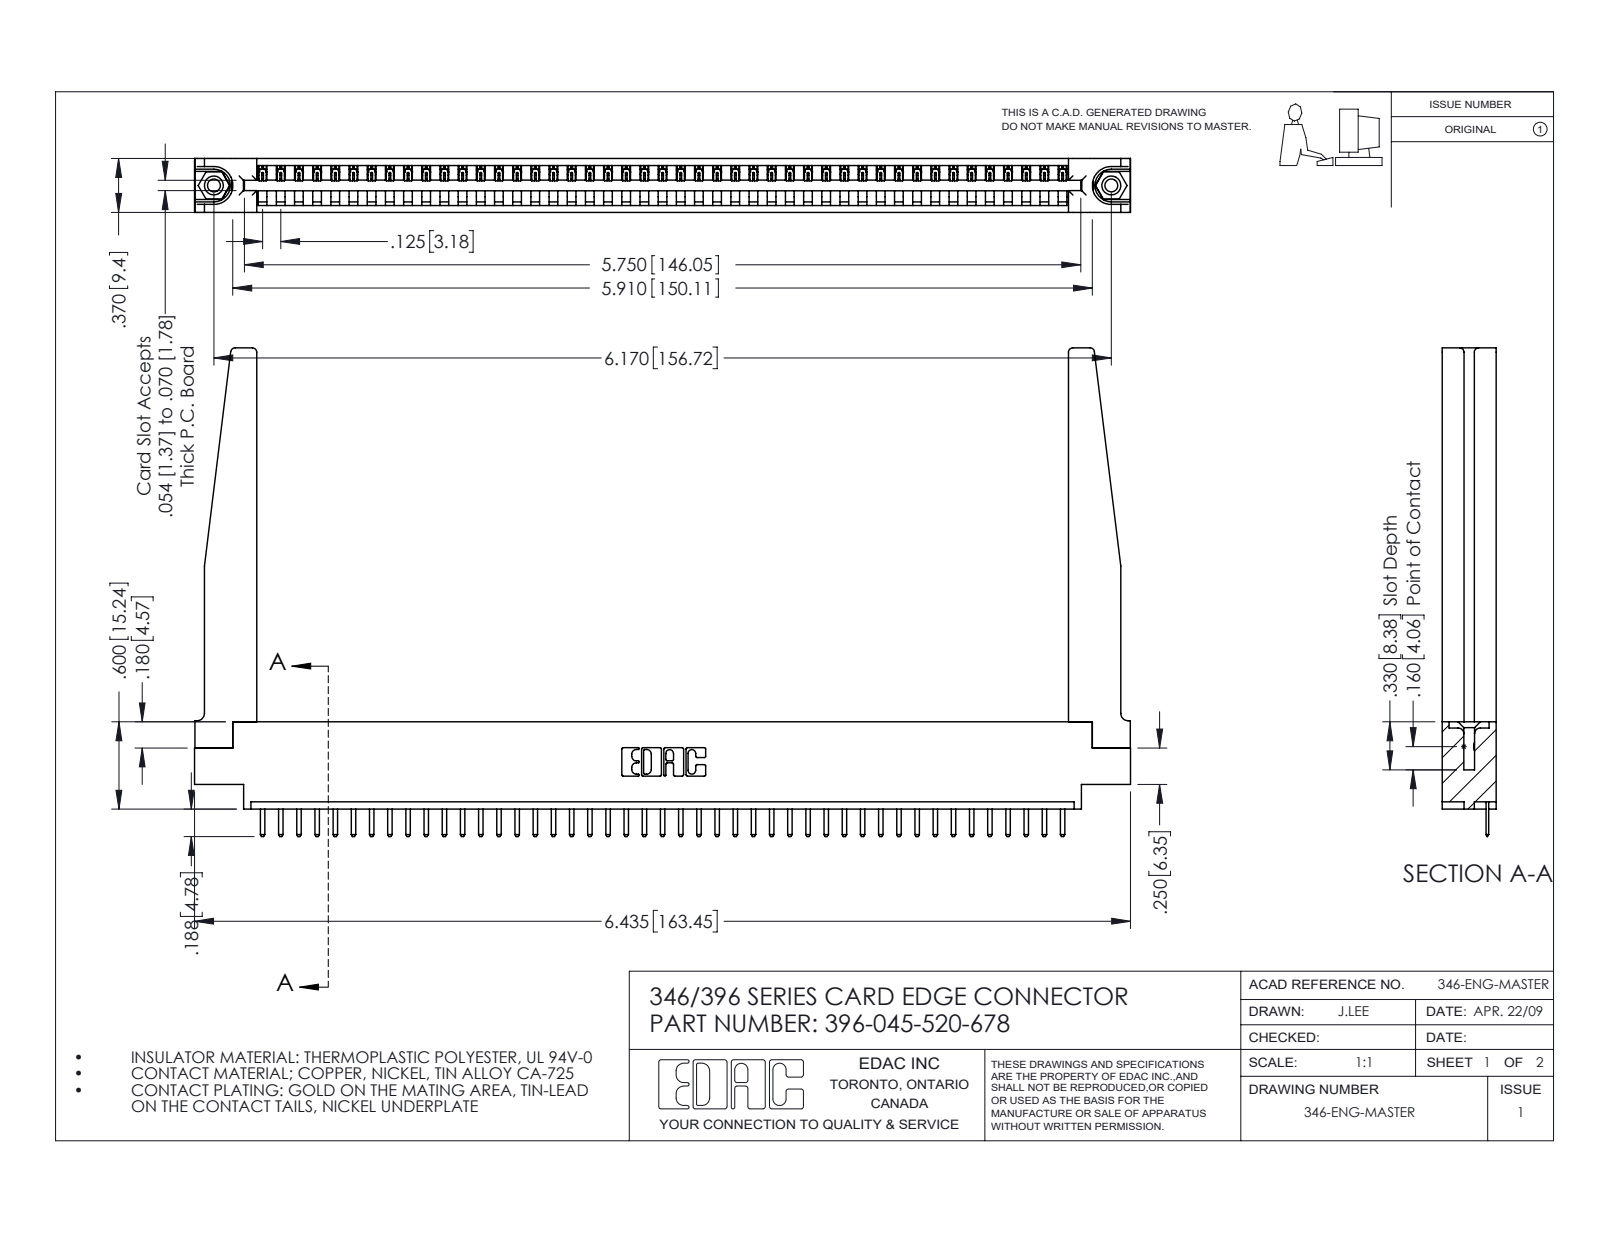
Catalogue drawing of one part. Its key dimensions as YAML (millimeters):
part_name: "345-250-001_345-250-001-102; 346 Part_0.170 Offset - 0.156 Dia-TH; 346-220-078_345-220-078; 345-292-001_345-293-120 (+1 more)"
step_written_by: "SolidWorks 2016 (CONFIG_CONTROL_DESIGN)"
units: millimeters
bodies: {solids: 50, faces: 3150, planar: 2112, cylindrical: 986, other: 52}
overall_size: [163.4, 85.3, 9.4]
volume: 22290
surface_area: 25530
round_holes:
  - {diameter: 2.3, count: 2}
  - {diameter: 3.2, count: 2}
  - {diameter: 4, count: 2}
  - {diameter: 1.6, count: 1}
round_bosses_or_shafts:
  - {diameter: 3.9, count: 2}
partial_cylinders:
  - {radius: 0.3, count: 92}
  - {radius: 0.2, count: 90}
  - {radius: 0.3, count: 22}
  - {radius: 0.8, count: 8}
  - {radius: 0.2, count: 6}
  - {radius: 0.8, count: 6}
  - {radius: 0.7, count: 3}
  - {radius: 0.8, count: 2}
face_to_face_distances: [9.4, 1.2, 8.2, 3.8, 1.8, 3.8, 6.4, 5.6, 2.5, 4.4]
hole_center_spacings: [6.2, 151.4, 156.7]
